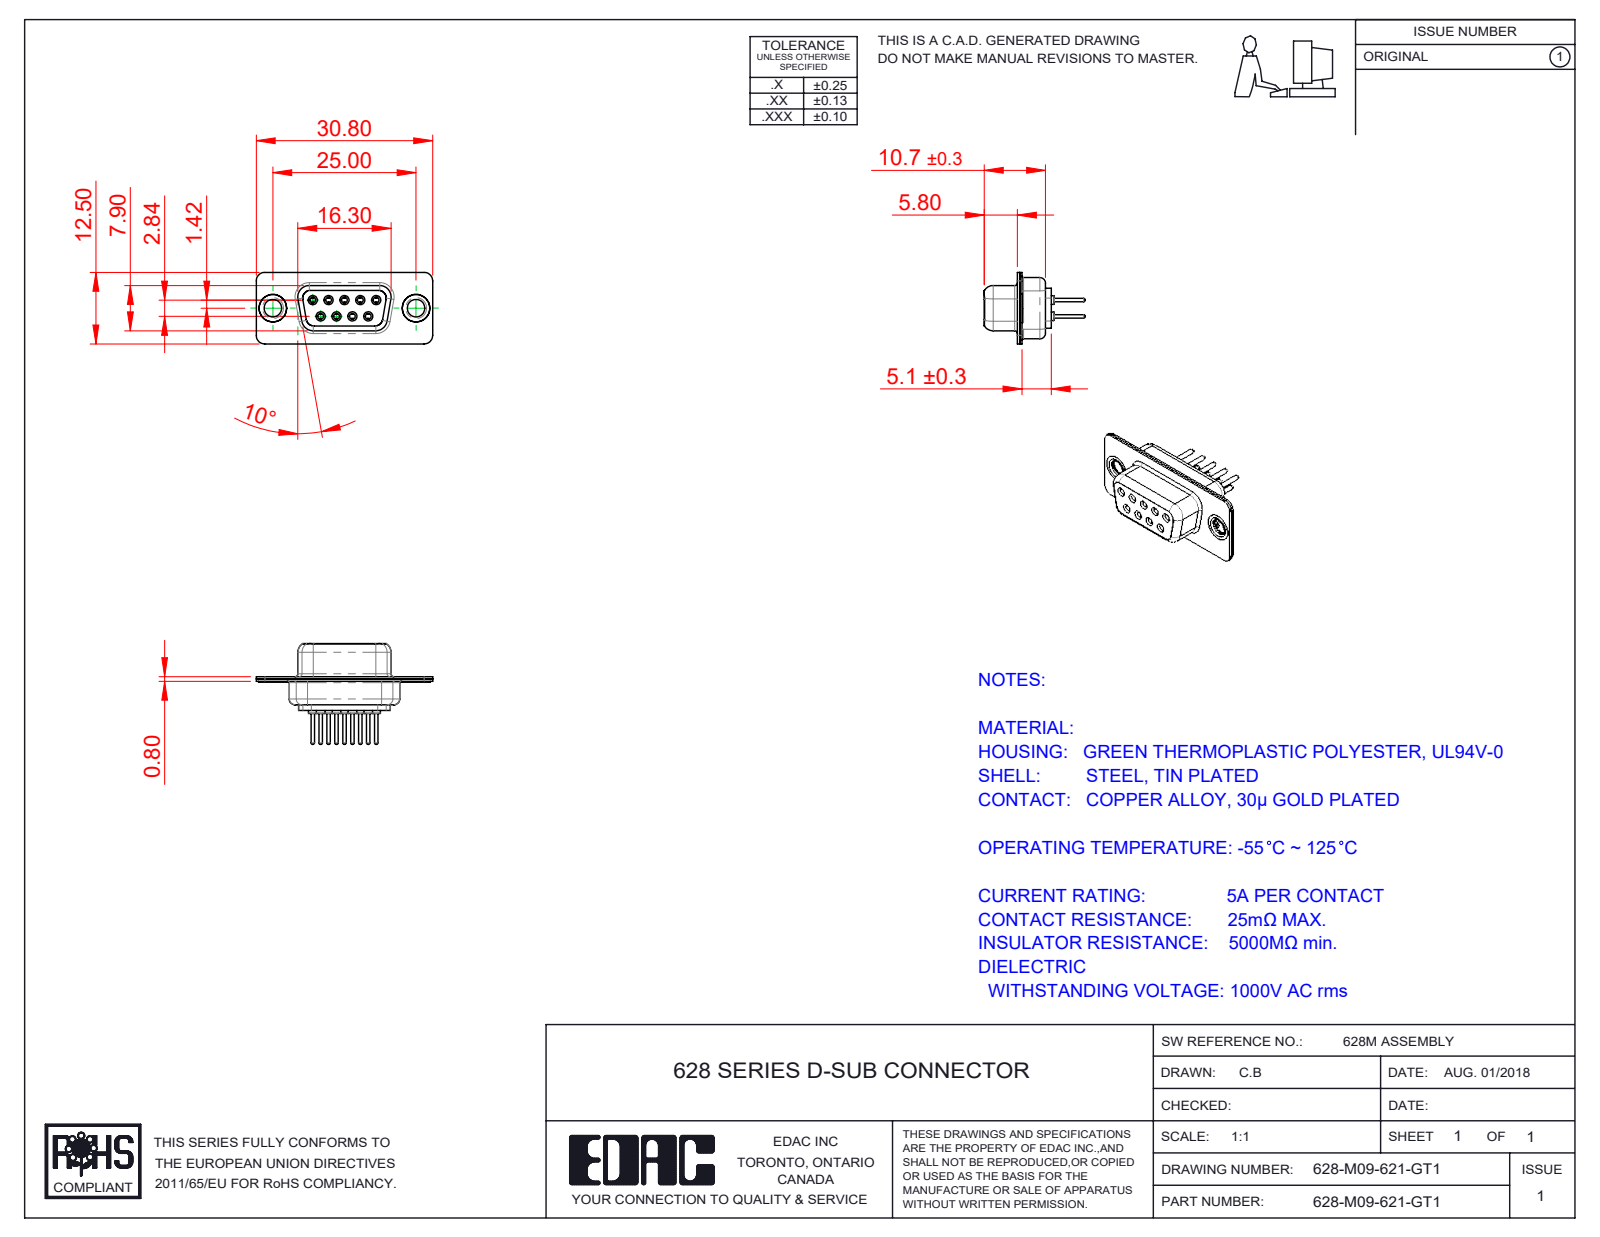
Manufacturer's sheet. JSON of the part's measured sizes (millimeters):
{"part_name": "628M Thru Hole Rivet; 628M Housing_09 Contacts; 628M Shell Rear_09 Contacts; 628M Contact Row 2_21 (+3 more)", "step_written_by": "SolidWorks 2020 (CONFIG_CONTROL_DESIGN)", "units": "millimeters", "bodies": {"solids": 14, "faces": 748, "planar": 202, "cylindrical": 292, "other": 254}, "overall_size": [30.8, 17.6, 12.5], "volume_mm3": 1624, "surface_area_mm2": 4277, "round_holes": [[1, 9], [1.1, 9], [1.7, 9], [1.8, 9], [2, 9], [3.05, 2], [4, 2], [4.8, 2]], "round_bosses_or_shafts": [[2.2, 9], [1.6, 9], [1.5, 9], [0.6, 9], [5, 2], [4.9, 2], [3.55, 2]], "partial_cylinders_radius": [[1.5, 16], [2, 12], [1.35, 8], [1.6, 8], [0.25, 4], [0.5, 4], [0.6, 4], [0.65, 4]], "face_to_face_distances": [0.4, 1.4, 0.45, 8.45, 0.8, 8.9, 1.8, 1, 6.2, 1.35], "hole_center_spacings": [3.16, 2.77, 5.54, 5.03, 5.04, 8.31, 7.1, 7.48]}
